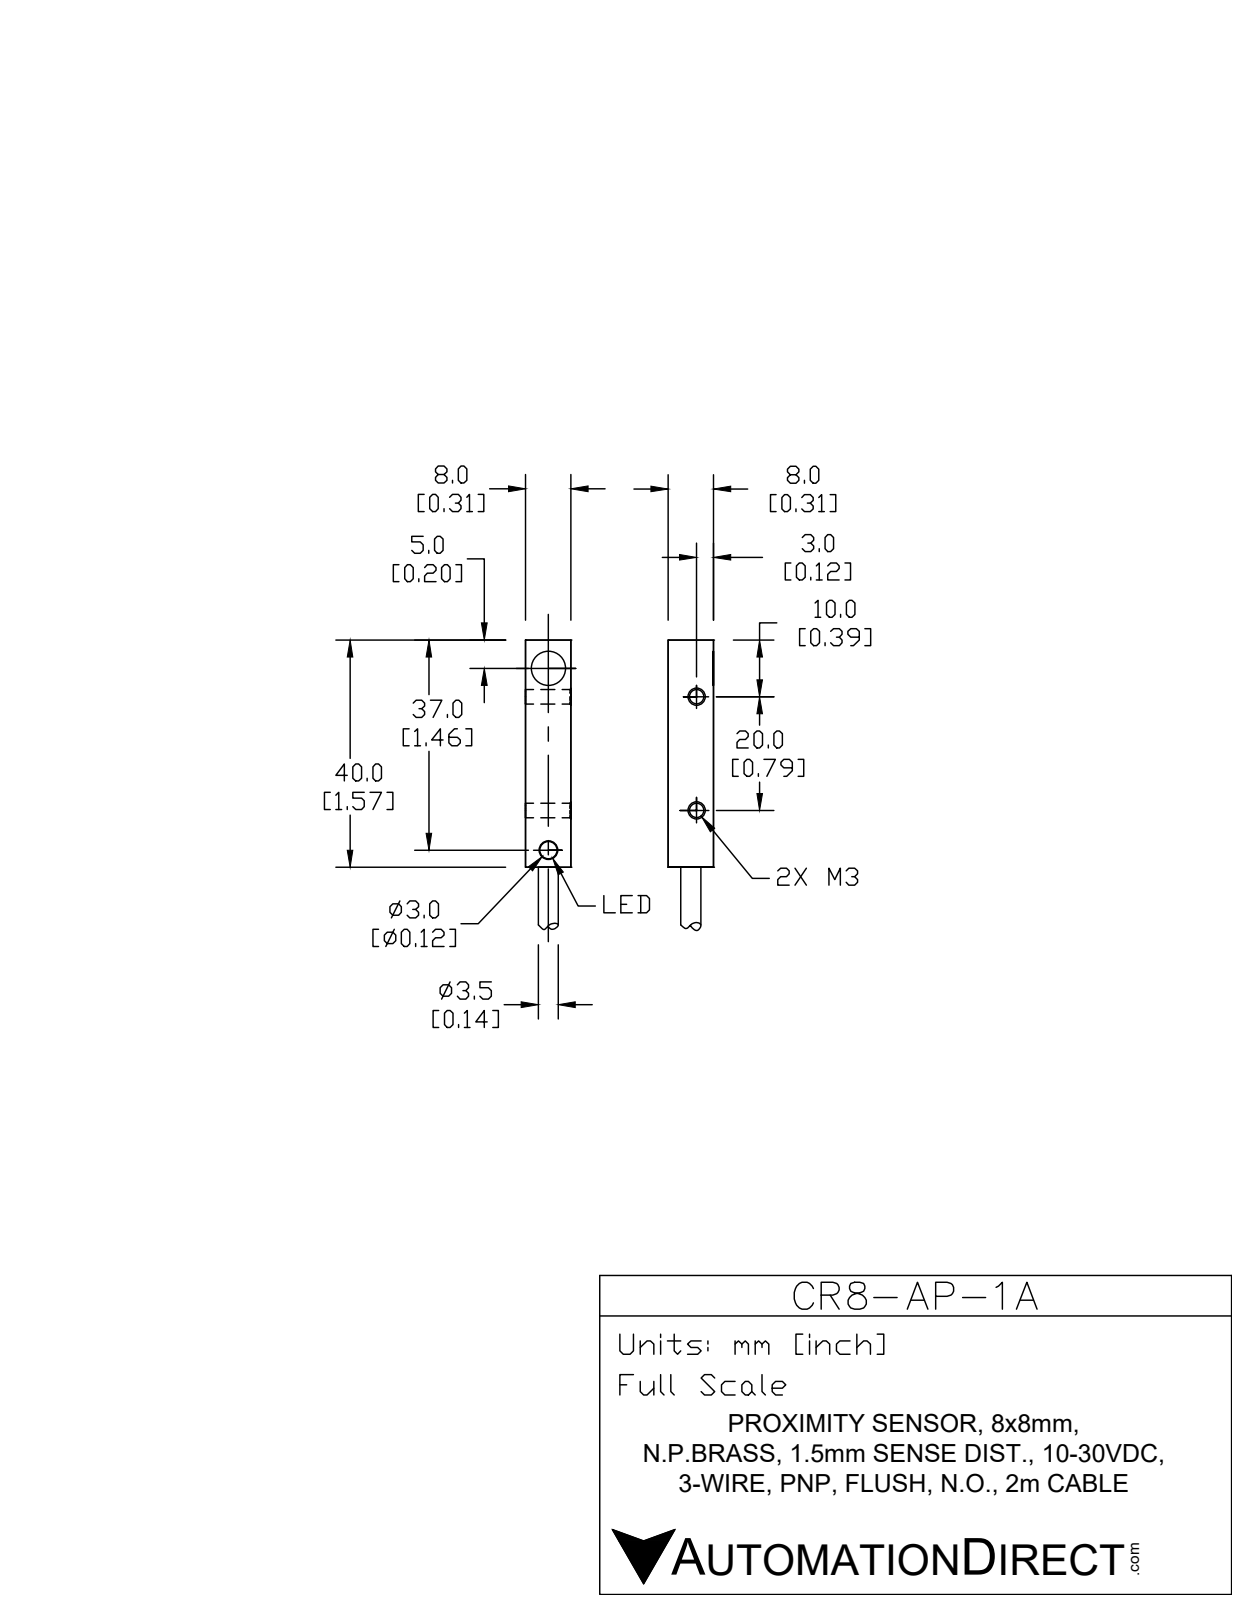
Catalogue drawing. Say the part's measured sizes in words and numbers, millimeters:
The part is named "CR8-AP-1A". Its 3-D file was written by "SolidWorks 2018 (AUTOMOTIVE_DESIGN)". It is 1 solid with 22 faces: 11 planar, 4 cylindrical and 7 other. Overall it measures 61.9 by 8 by 8 millimeters. Its volume is 2 650 cubic millimeters and its surface area 1 762 square millimeters. Round holes: 2 of diameter 2.5. Round bosses or shafts: 1 of diameter 3.5. Partial cylindrical surfaces (rounded edges, fillets, slot ends): 1 of radius 3.4. The main face-to-face distances are 8, 7.9, 40, 7.8, 7.9, 0.6, 7.4, 6.9, 0.7, 39.3. The hole center spacings are 20.
